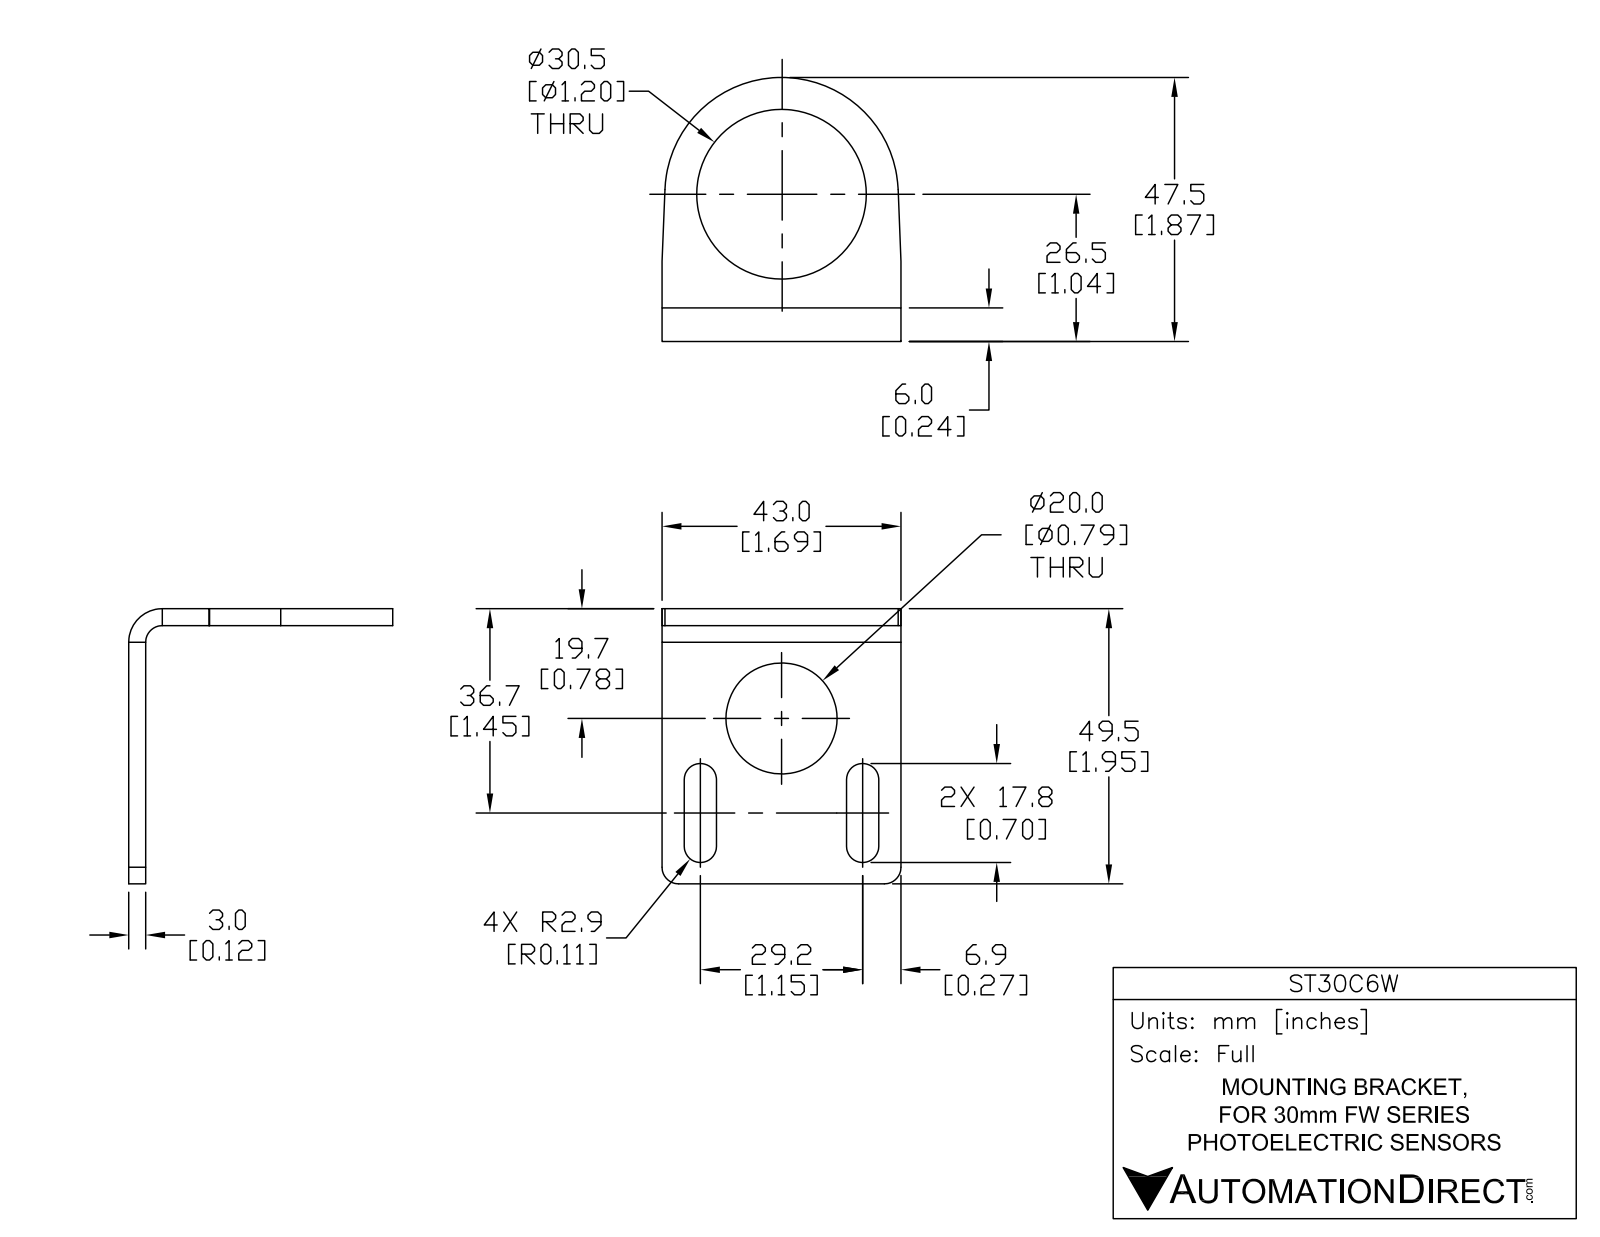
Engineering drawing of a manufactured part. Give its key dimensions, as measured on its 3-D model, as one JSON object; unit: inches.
{"part_name": "ST30C6W", "step_written_by": "SolidWorks 2013 (AUTOMOTIVE_DESIGN)", "units": "inches", "bodies": {"solids": 1, "faces": 29, "planar": 13, "cylindrical": 16, "other": 0}, "overall_size": [1.95, 1.865, 1.69], "volume_in3": 0.464, "surface_area_in2": 10.05, "round_holes": [[0.79, 1], [1.2, 1]], "partial_cylinders_radius": [[0.11, 4], [0.12, 3], [0.24, 1], [0.825, 1]], "face_to_face_distances": [0.12, 1.69, 1.83, 1.95, 0.22, 1.15, 1.53, 0.16, 0.16, 1.31]}
